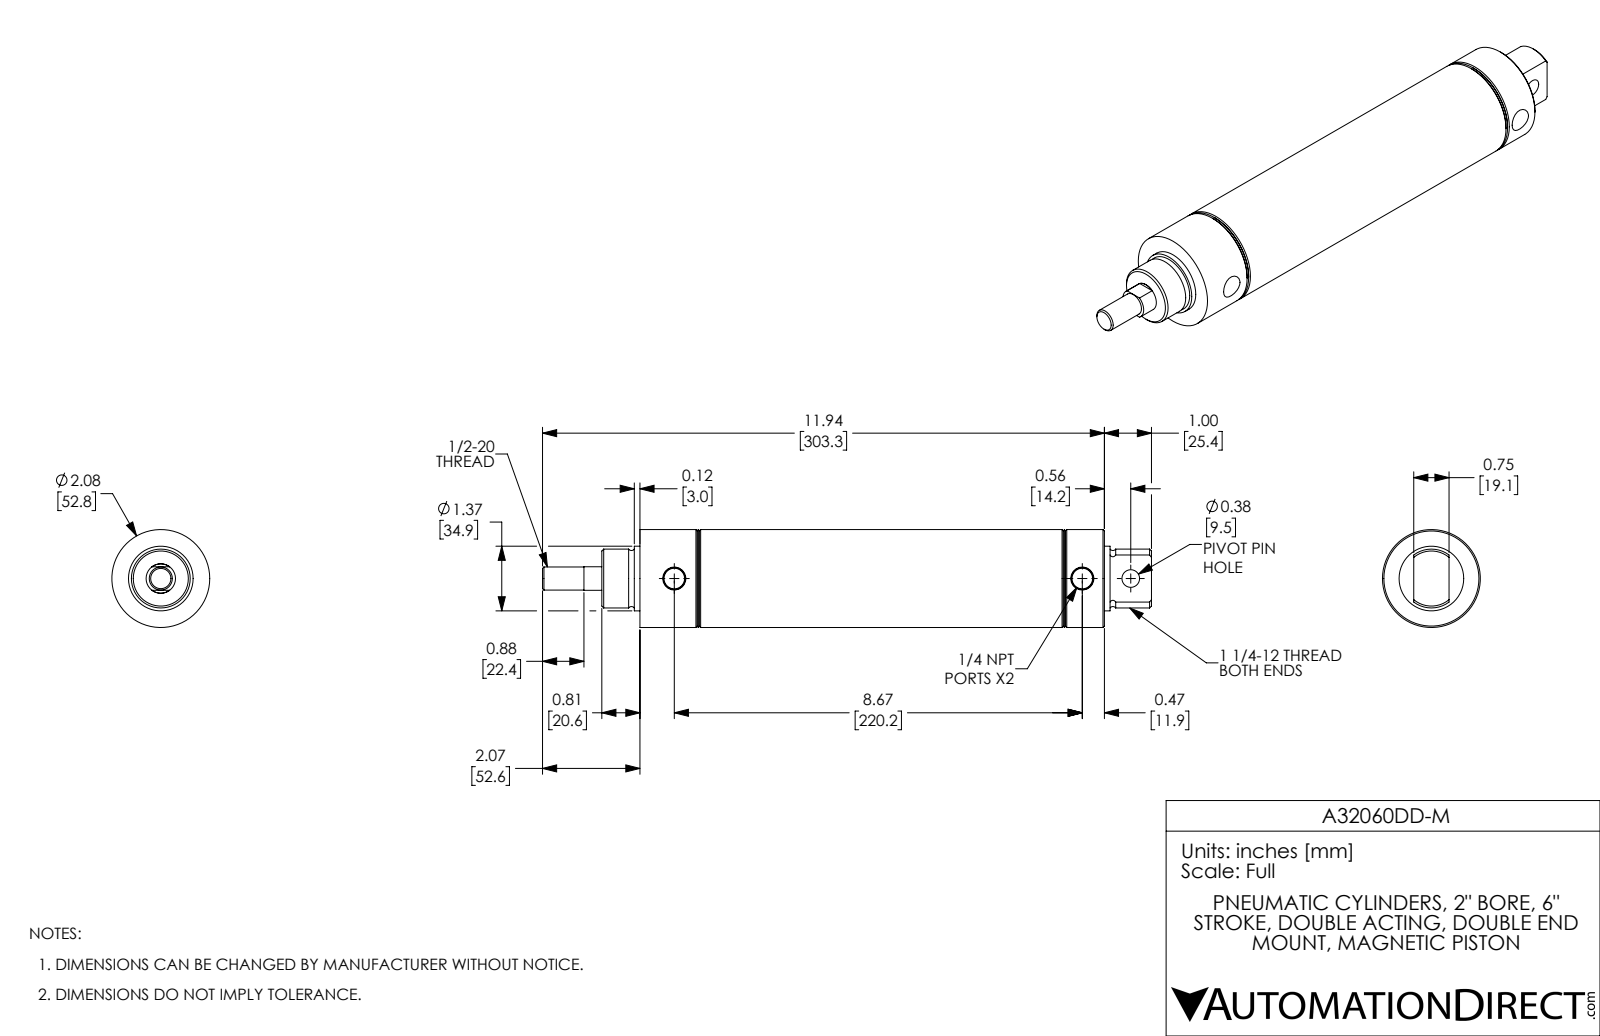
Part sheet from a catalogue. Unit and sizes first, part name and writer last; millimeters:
Units: millimetres
Overall size (bounding box): 328.7 × 52.8 × 52.8
Round holes (diameter × count): ⌀11.1 ×2, ⌀9.5 ×1, ⌀15.9 ×1, ⌀50.8 ×1
Round bosses / shafts (diameter × count): ⌀52.8 ×1, ⌀34.9 ×1, ⌀31.8 ×1, ⌀12.5 ×1
Main face-to-face distances: 42.8, 207.9, 12.7, 165.1, 152.4, 195.2, 55.5, 250.7, 3, 45.8
Hole centre spacings: 26.2, 220.2, 246.4
Volume: 300 900 mm³ · Surface area: 103 900 mm²
Bodies: 2 solids, 88 faces (20 planar, 30 cylindrical, 38 other)
Part name (STEP PRODUCT): A32060DD-M; A32060DD-M-Rod; A32060DD-M-MainBody
STEP written by: SolidWorks 2017 (AUTOMOTIVE_DESIGN)
